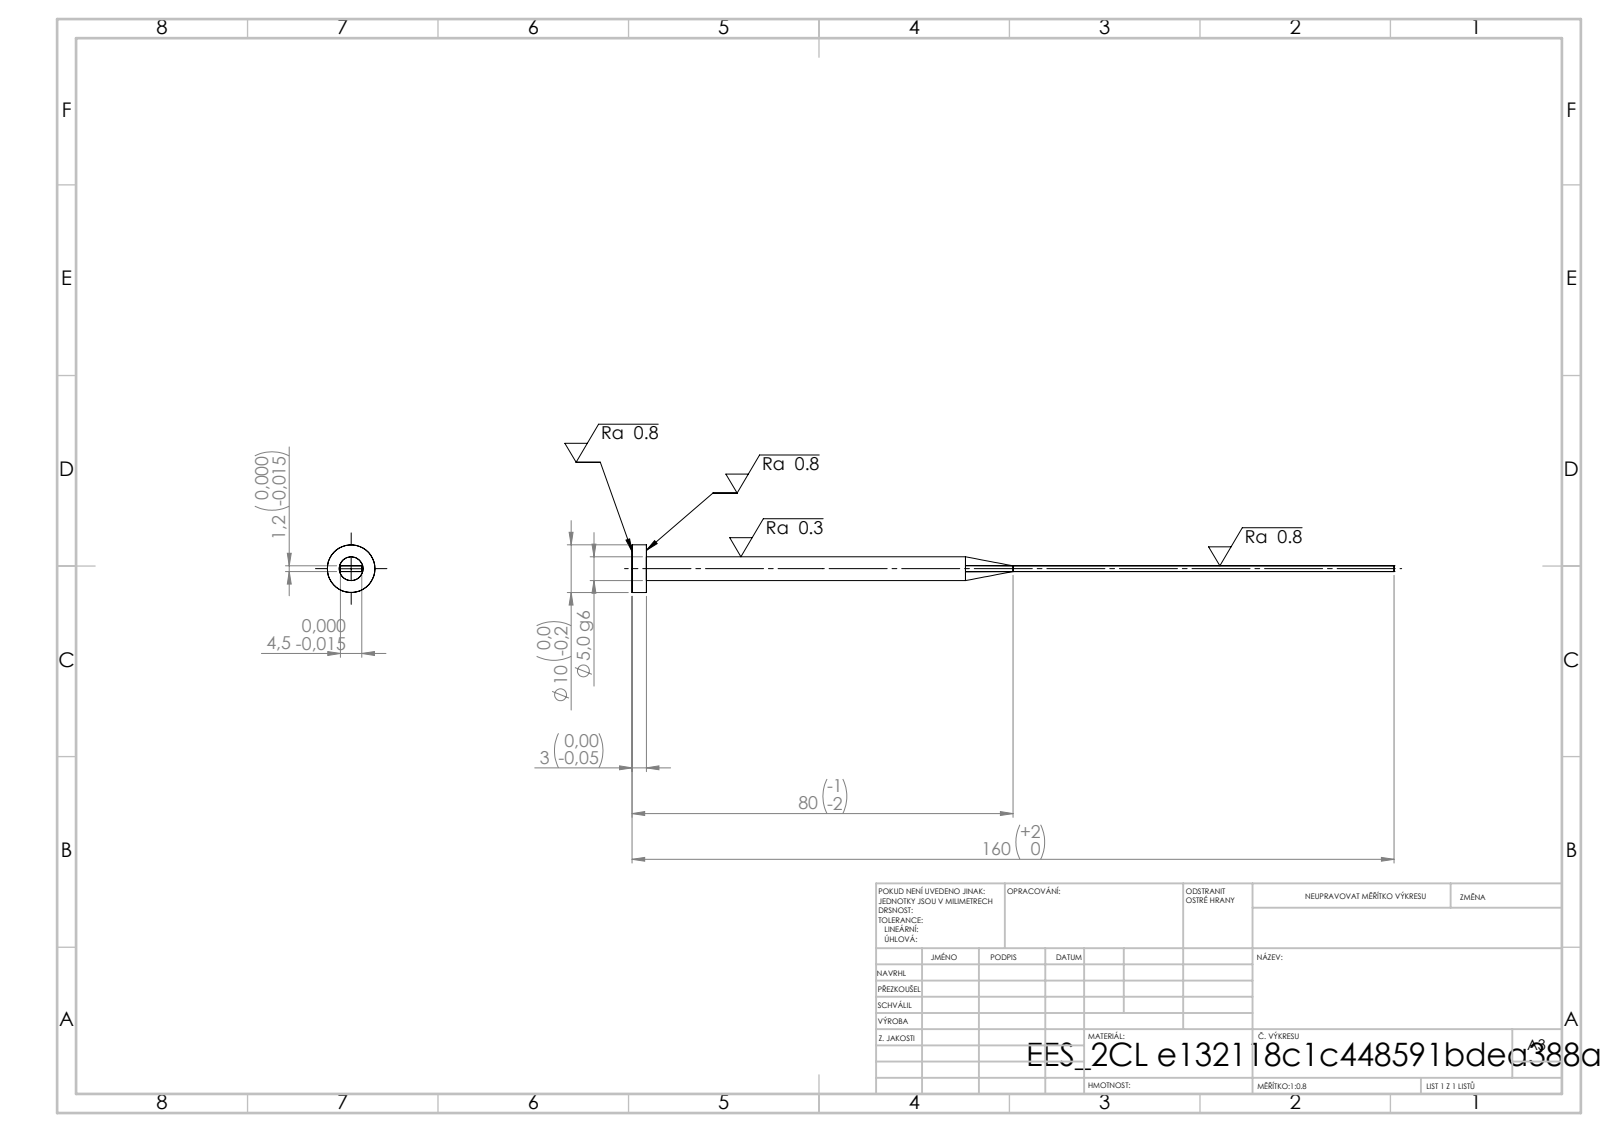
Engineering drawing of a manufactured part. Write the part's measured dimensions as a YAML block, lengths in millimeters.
step_written_by: "SolidWorks 2019 (CONFIG_CONTROL_DESIGN)"
units: millimeters
bodies: {solids: 1, faces: 15, planar: 7, cylindrical: 4, other: 4}
overall_size: [160, 10, 10]
volume: 2103
surface_area: 2333
round_bosses_or_shafts:
  - {diameter: 10, count: 1}
  - {diameter: 5, count: 1}
face_to_face_distances: [1.2, 4.5, 3, 160, 157]
